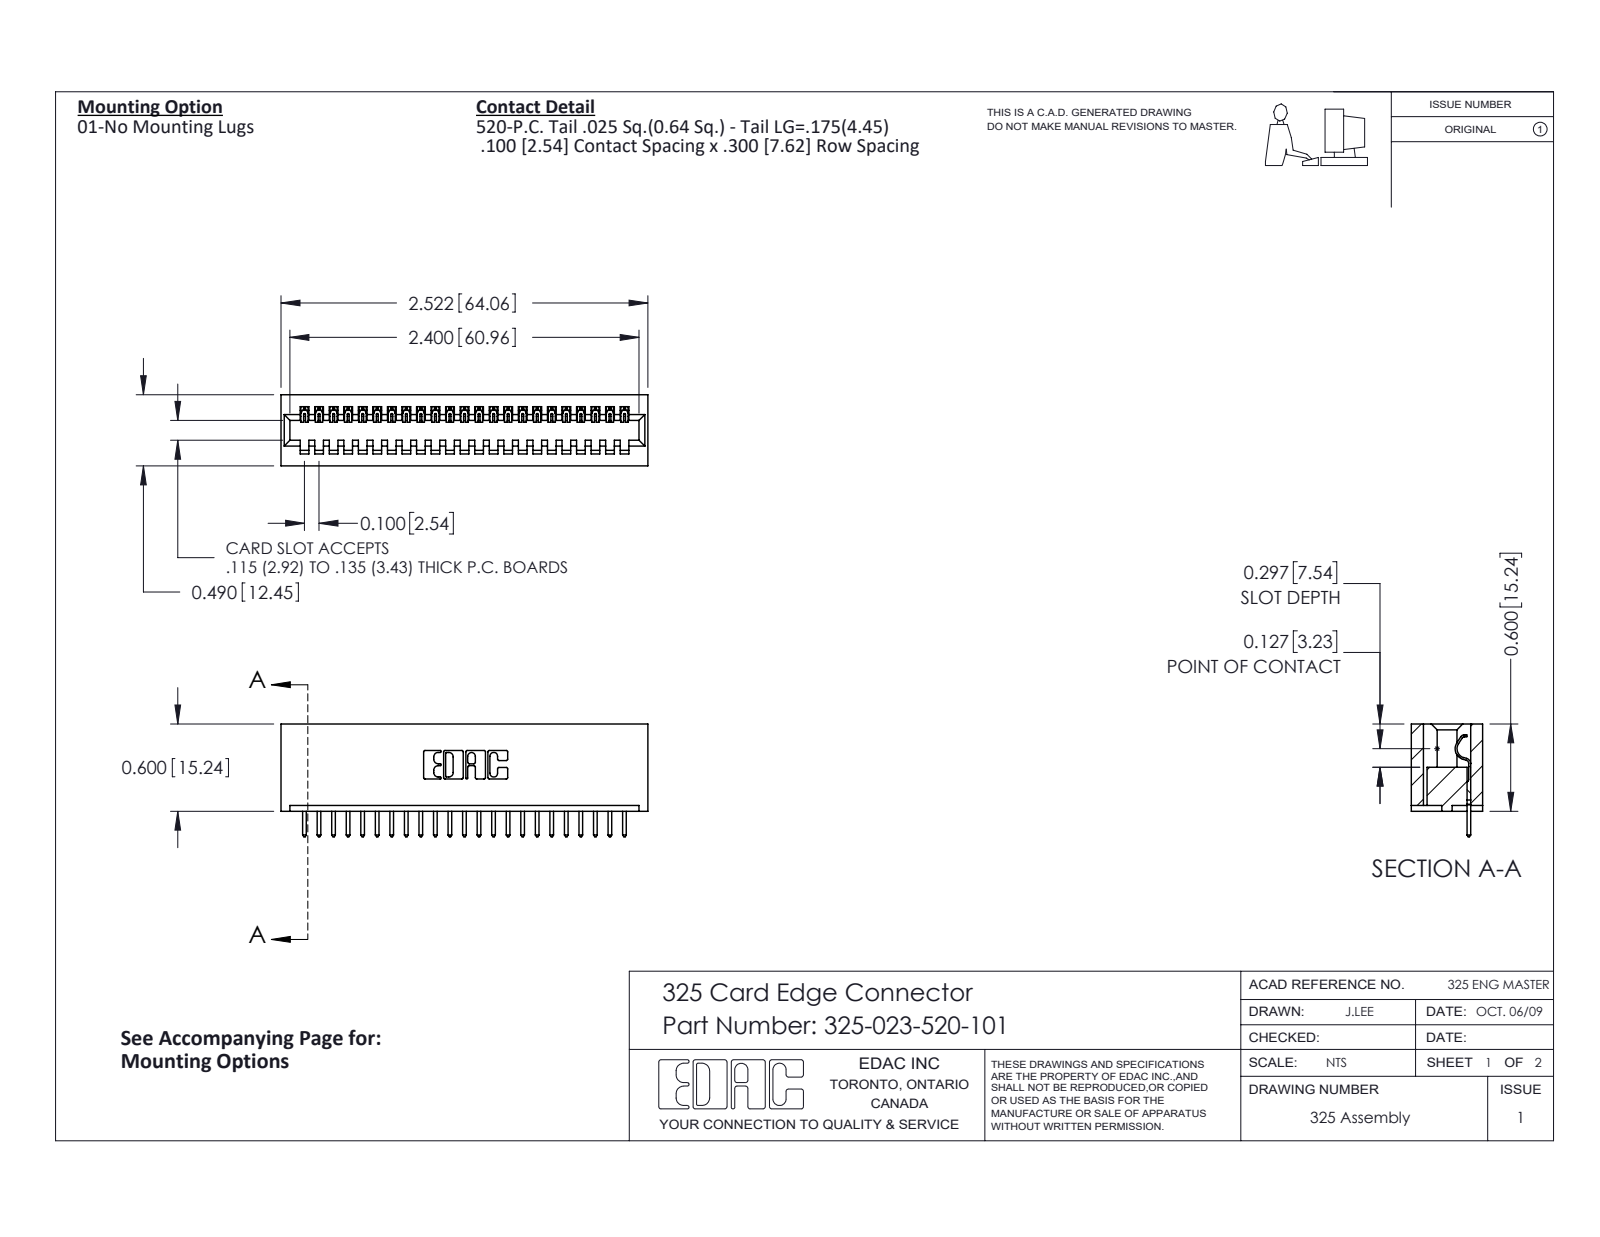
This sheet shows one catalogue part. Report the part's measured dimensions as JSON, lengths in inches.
{"part_name": "325 Part_Lugless; 325-023-520-101; 325-292-001_325-293-120", "step_written_by": "SolidWorks 2016 (CONFIG_CONTROL_DESIGN)", "units": "inches", "bodies": {"solids": 24, "faces": 1440, "planar": 1032, "cylindrical": 408, "other": 0}, "overall_size": [2.522, 0.775, 0.49], "volume_in3": 0.518, "surface_area_in2": 14.27, "partial_cylinders_radius": [[0.006, 46], [0.01, 46], [0.01, 22], [0.007, 6], [0.031, 6], [0.026, 3], [0.014, 1], [0.022, 1]], "face_to_face_distances": [0.083, 0.407, 0.3, 0.49, 0.107, 0.383, 0.025, 0.56, 0.325, 0.1]}
